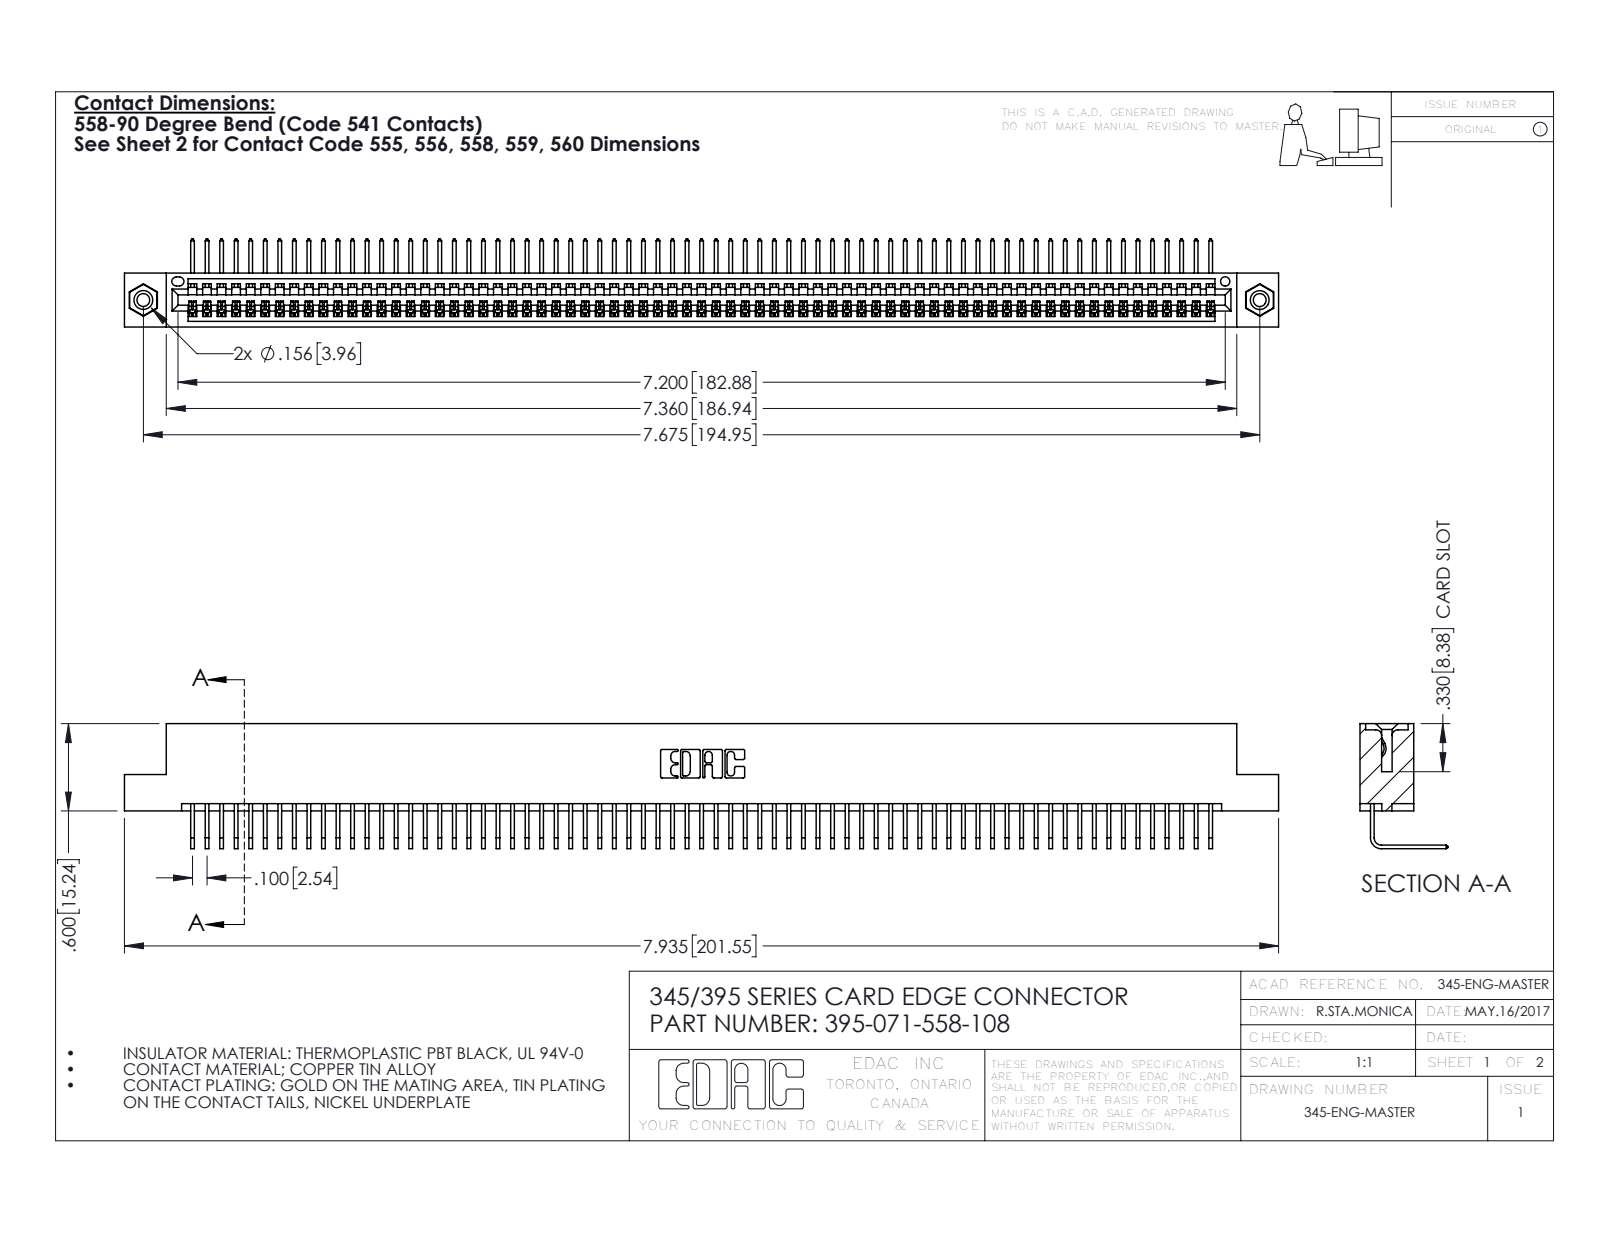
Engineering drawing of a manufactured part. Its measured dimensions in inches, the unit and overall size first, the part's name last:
Units: inches
Overall size (bounding box): 7.935 × 0.859 × 0.605
Round holes (diameter × count): ⌀0.089 ×2, ⌀0.125 ×2, ⌀0.156 ×2, ⌀0.064 ×1
Round bosses / shafts (diameter × count): ⌀0.155 ×2
Partial cylindrical surfaces — rounded edges, fillets, slot ends (radius × count): R0.006 ×142, R0.01 ×22, R0.007 ×6, R0.031 ×6, R0.026 ×3, R0.031 ×2, R0.04 ×2, R0.014 ×1
Main face-to-face distances: 0.072, 0.298, 0.37, 0.2, 0.098, 0.272, 0.025, 0.225, 0.149, 0.072
Hole centre spacings: 0.27, 7.439, 7.675
Volume: 1.197 in³ · Surface area: 43.19 in²
Bodies: 74 solids, 4446 faces (3094 planar, 1336 cylindrical, 16 other)
Part name (STEP PRODUCT): 345-292-001_558 Tail - 2; 345 Part_Flush Mounting Lugs - 0.156 Dia-TI; 345-250-001_345-250-003-102; 395-071-558-108
STEP written by: SolidWorks 2016 (CONFIG_CONTROL_DESIGN)
